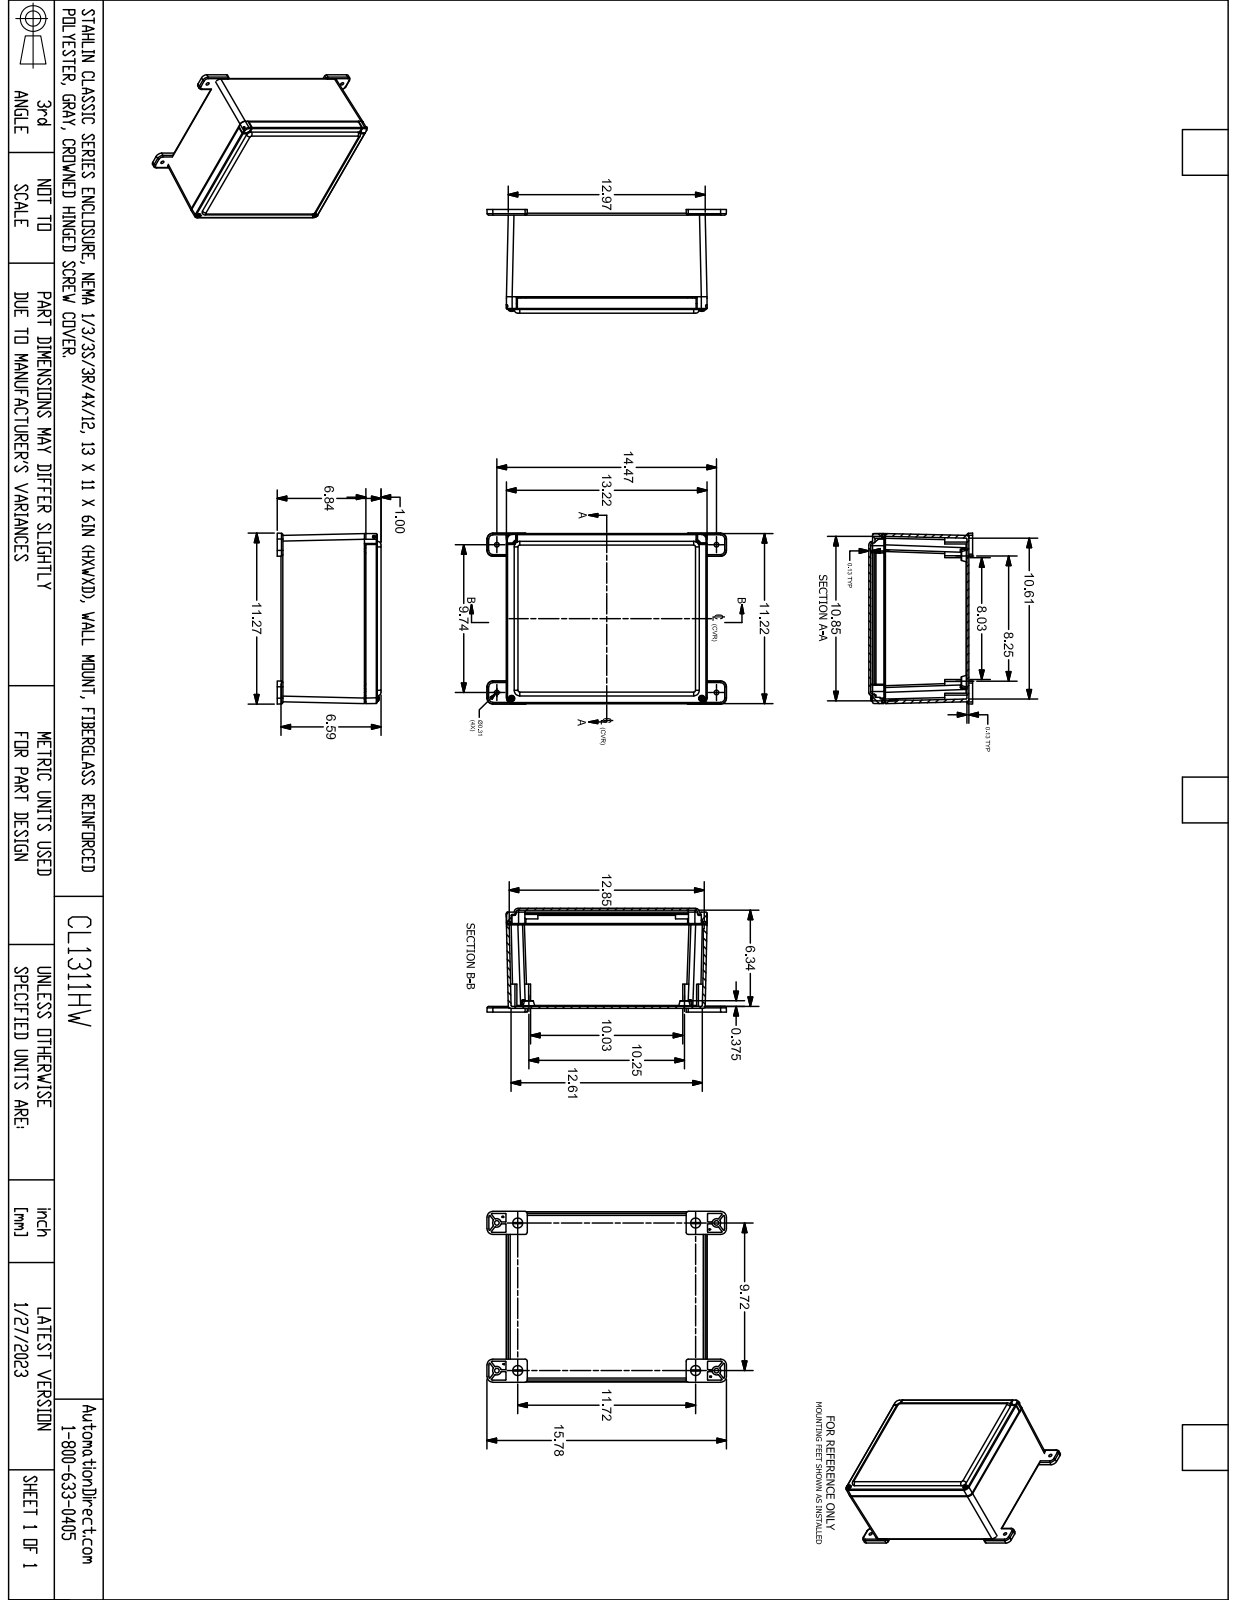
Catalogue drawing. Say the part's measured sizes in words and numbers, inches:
The part is named "CE1311HW". Its 3-D file was written by "SolidWorks 2018 (AUTOMOTIVE_DESIGN)". It is 29 solids with 1474 faces: 646 planar, 416 cylindrical and 412 other. Overall it measures 15.781 by 11.271 by 6.844 inches. Its volume is 113.7 cubic inches and its surface area 1 349 square inches. Round holes: 6 of diameter 0.159, 6 of diameter 0.281, 4 of diameter 0.156, 4 of diameter 0.313, 4 of diameter 0.313, 4 of diameter 0.344, 4 of diameter 0.531, 2 of diameter 0.096, 2 of diameter 0.19, 2 of diameter 0.219, 2 of diameter 0.23, 2 of diameter 0.28. Round bosses or shafts: 6 of diameter 0.27, 4 of diameter 0.229, 2 of diameter 0.375, 2 of diameter 0.373, 2 of diameter 0.136, 1 of diameter 0.325, 1 of diameter 0.182, 1 of diameter 0.127. Partial cylindrical surfaces (rounded edges, fillets, slot ends): 60 of radius 0.031, 56 of radius 0.031, 42 of radius 0.125, 26 of radius 0.062, 16 of radius 0.25, 13 of radius 0.1, 10 of radius 0.375, 8 of radius 0.059. The main face-to-face distances are 0.125, 6.469, 0.186, 6.594, 6.344, 0.125, 0.25, 6.344, 6.219, 0.75. The hole center spacings are 1.046, 11.447, 12.131, 13.506, 12.531, 0.574, 1.039, 1.375.
